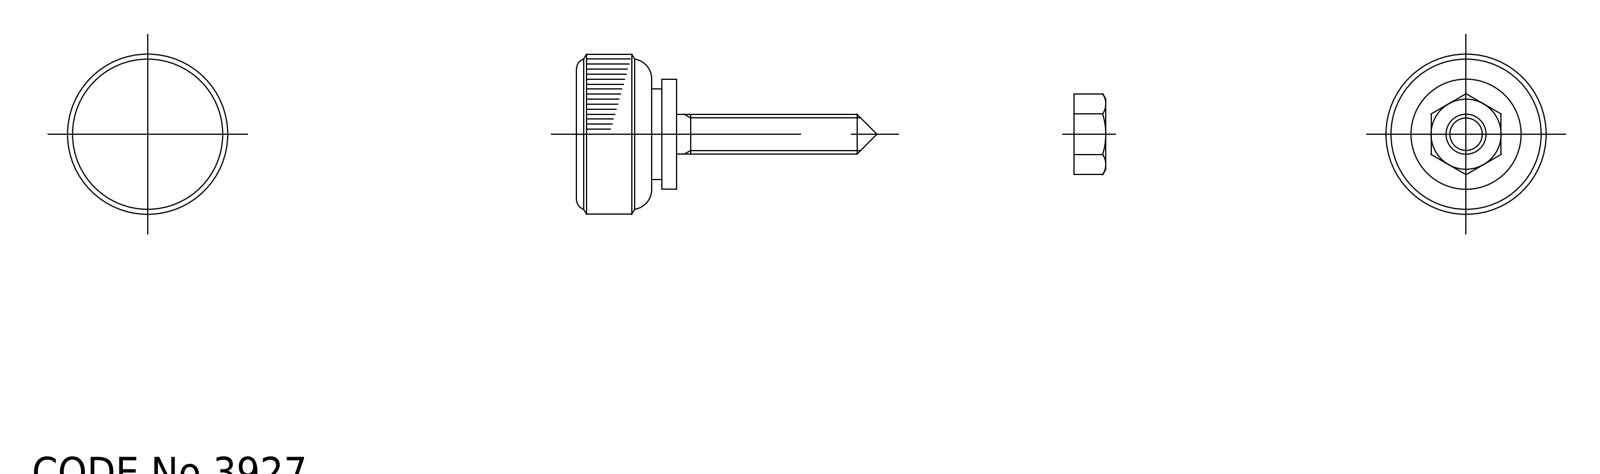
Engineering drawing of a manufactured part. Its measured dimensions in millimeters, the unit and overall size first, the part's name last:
Units: millimetres
Overall size (bounding box): 30 × 16 × 16
Volume: 1 935 mm³ · Surface area: 1 240 mm²
Bodies: 2 solids, 36 faces (0 planar, 0 cylindrical, 36 other)
Part name (STEP PRODUCT): nut; knob; THA_188_1_1415_36
STEP written by: CADfix (AUTOMOTIVE_DESIGN)
